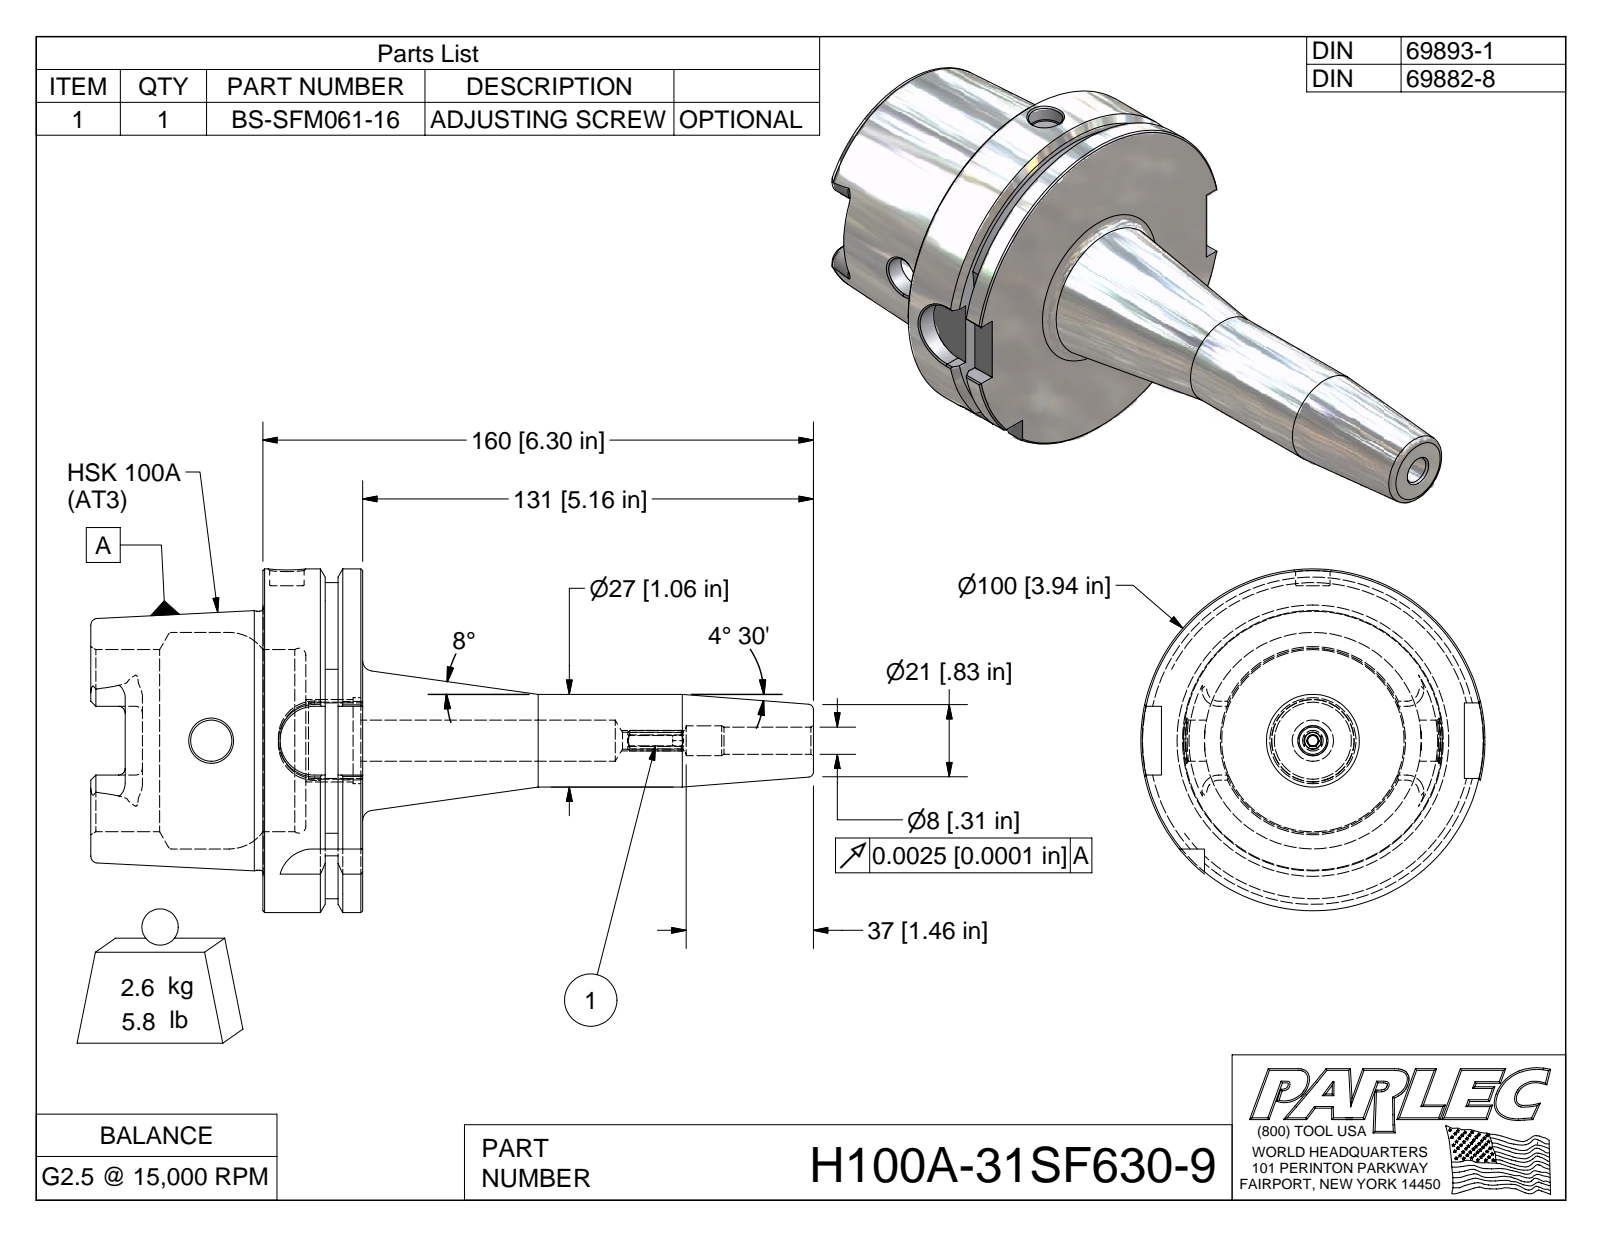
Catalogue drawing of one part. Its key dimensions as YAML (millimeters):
part_name: "H100A-31SF630-9; H100A-31SF630-9-1; BS-SFM061-16"
step_written_by: "Autodesk Inventor 2009 (AUTOMOTIVE_DESIGN)"
units: millimeters
bodies: {solids: 2, faces: 155, planar: 49, cylindrical: 30, other: 76}
overall_size: [210, 100, 100]
volume: 332300
surface_area: 65350
round_holes:
  - {diameter: 7.9, count: 1}
  - {diameter: 8.7, count: 1}
  - {diameter: 10, count: 1}
  - {diameter: 12, count: 1}
  - {diameter: 22.4, count: 1}
  - {diameter: 25, count: 1}
  - {diameter: 53, count: 1}
  - {diameter: 63, count: 1}
round_bosses_or_shafts:
  - {diameter: 100, count: 1}
  - {diameter: 75.4, count: 1}
  - {diameter: 27, count: 1}
partial_cylinders:
  - {radius: 10, count: 4}
  - {radius: 2, count: 3}
  - {radius: 4.9, count: 2}
  - {radius: 3, count: 1}
  - {radius: 46, count: 1}
face_to_face_distances: [29, 12.5, 16.5, 50, 62.5, 79, 68.1, 18.1, 5.6, 10.9]
